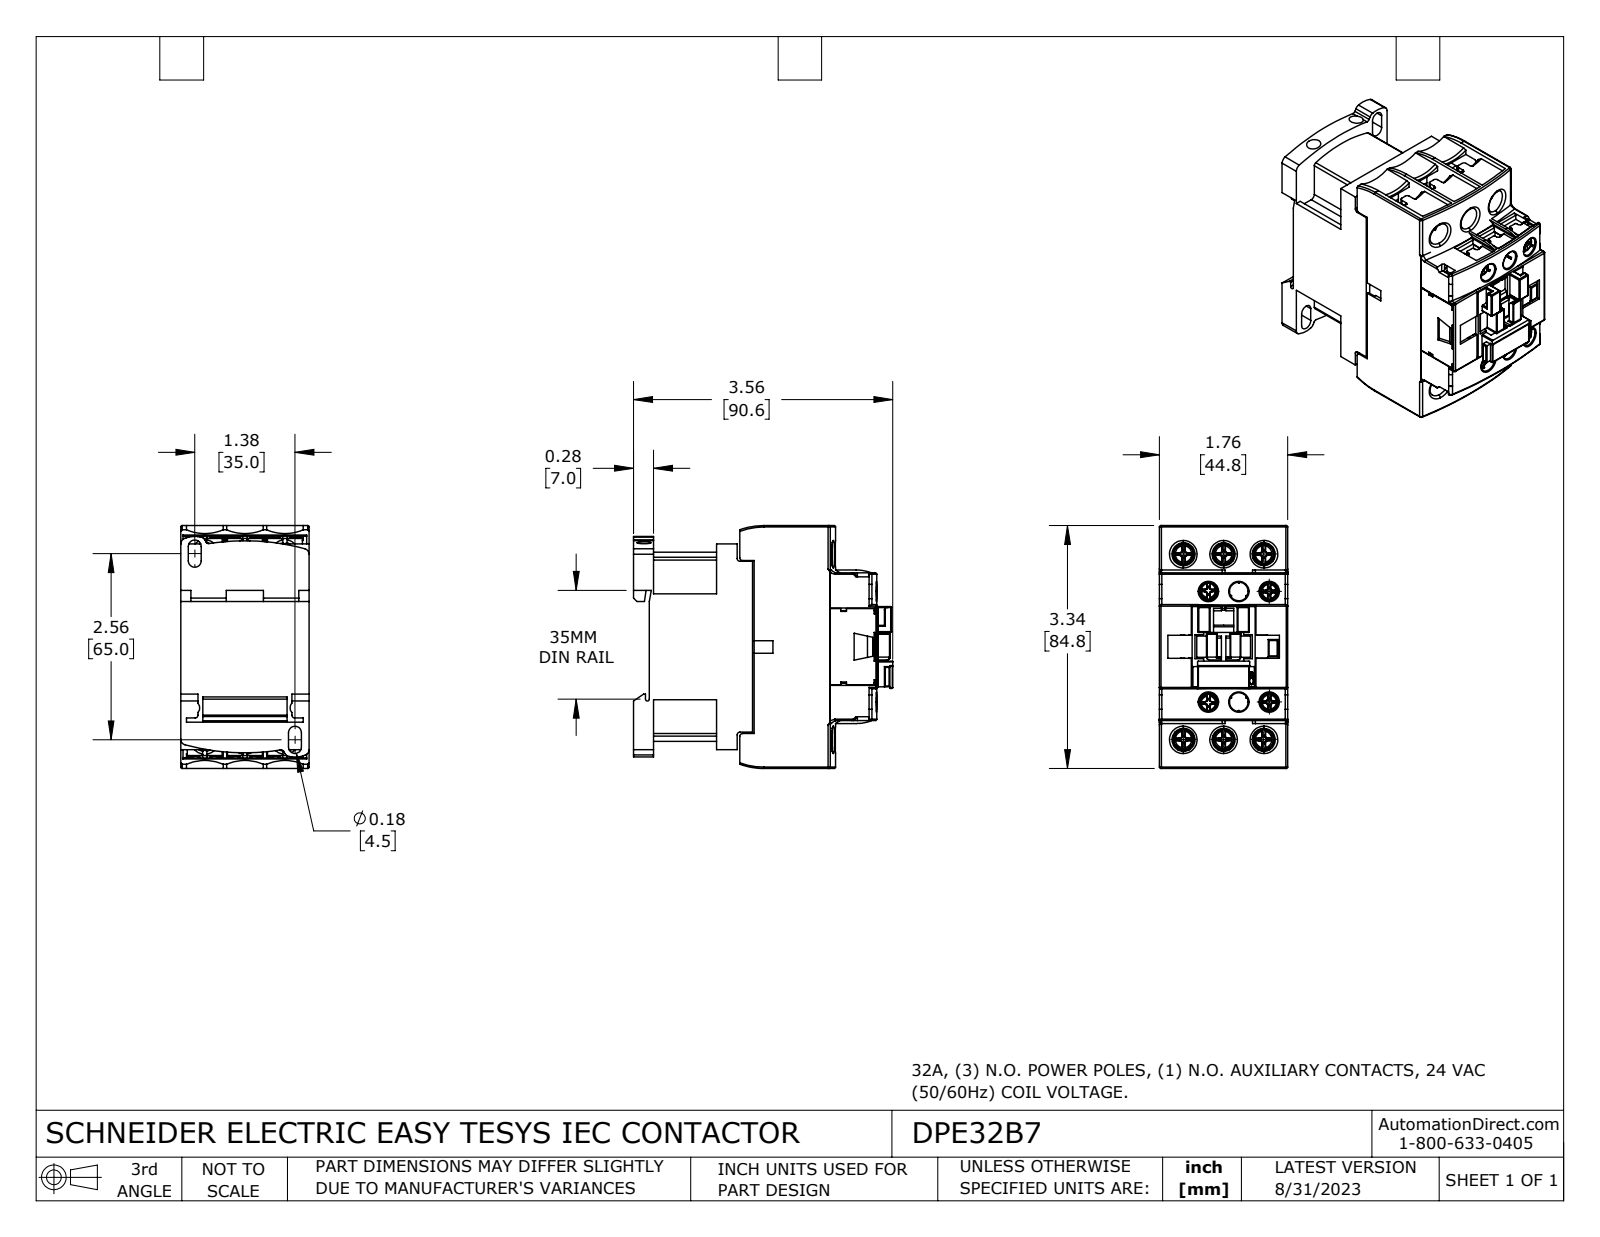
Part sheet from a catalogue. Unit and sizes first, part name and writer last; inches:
Units: inches
Overall size (bounding box): 3.565 × 3.339 × 1.764
Round holes (diameter × count): ⌀0.256 ×6, ⌀0.315 ×6, ⌀0.197 ×2
Round bosses / shafts (diameter × count): ⌀0.157 ×8, ⌀0.126 ×6, ⌀0.138 ×4, ⌀0.134 ×4, ⌀0.108 ×4, ⌀0.394 ×3
Partial cylindrical surfaces — rounded edges, fillets, slot ends (radius × count): R0.012 ×58, R0.006 ×36, R0.039 ×36, R0.02 ×34, R0.63 ×18, R0.008 ×17, R0.079 ×9, R0.031 ×8
Main face-to-face distances: 1.764, 0.551, 0.022, 0.059, 1.089, 1.067, 0.047, 0.031, 1.382, 1.419
Hole centre spacings: 0.417, 0.551, 1.576, 2.61, 1.52, 2.551, 0.553, 0.56
Volume: 12.56 in³ · Surface area: 100.4 in²
Bodies: 16 solids, 2674 faces (1724 planar, 584 cylindrical, 366 other)
Part name (STEP PRODUCT): DPE32B7
STEP written by: SolidWorks 2021 (CONFIG_CONTROL_DESIGN)
